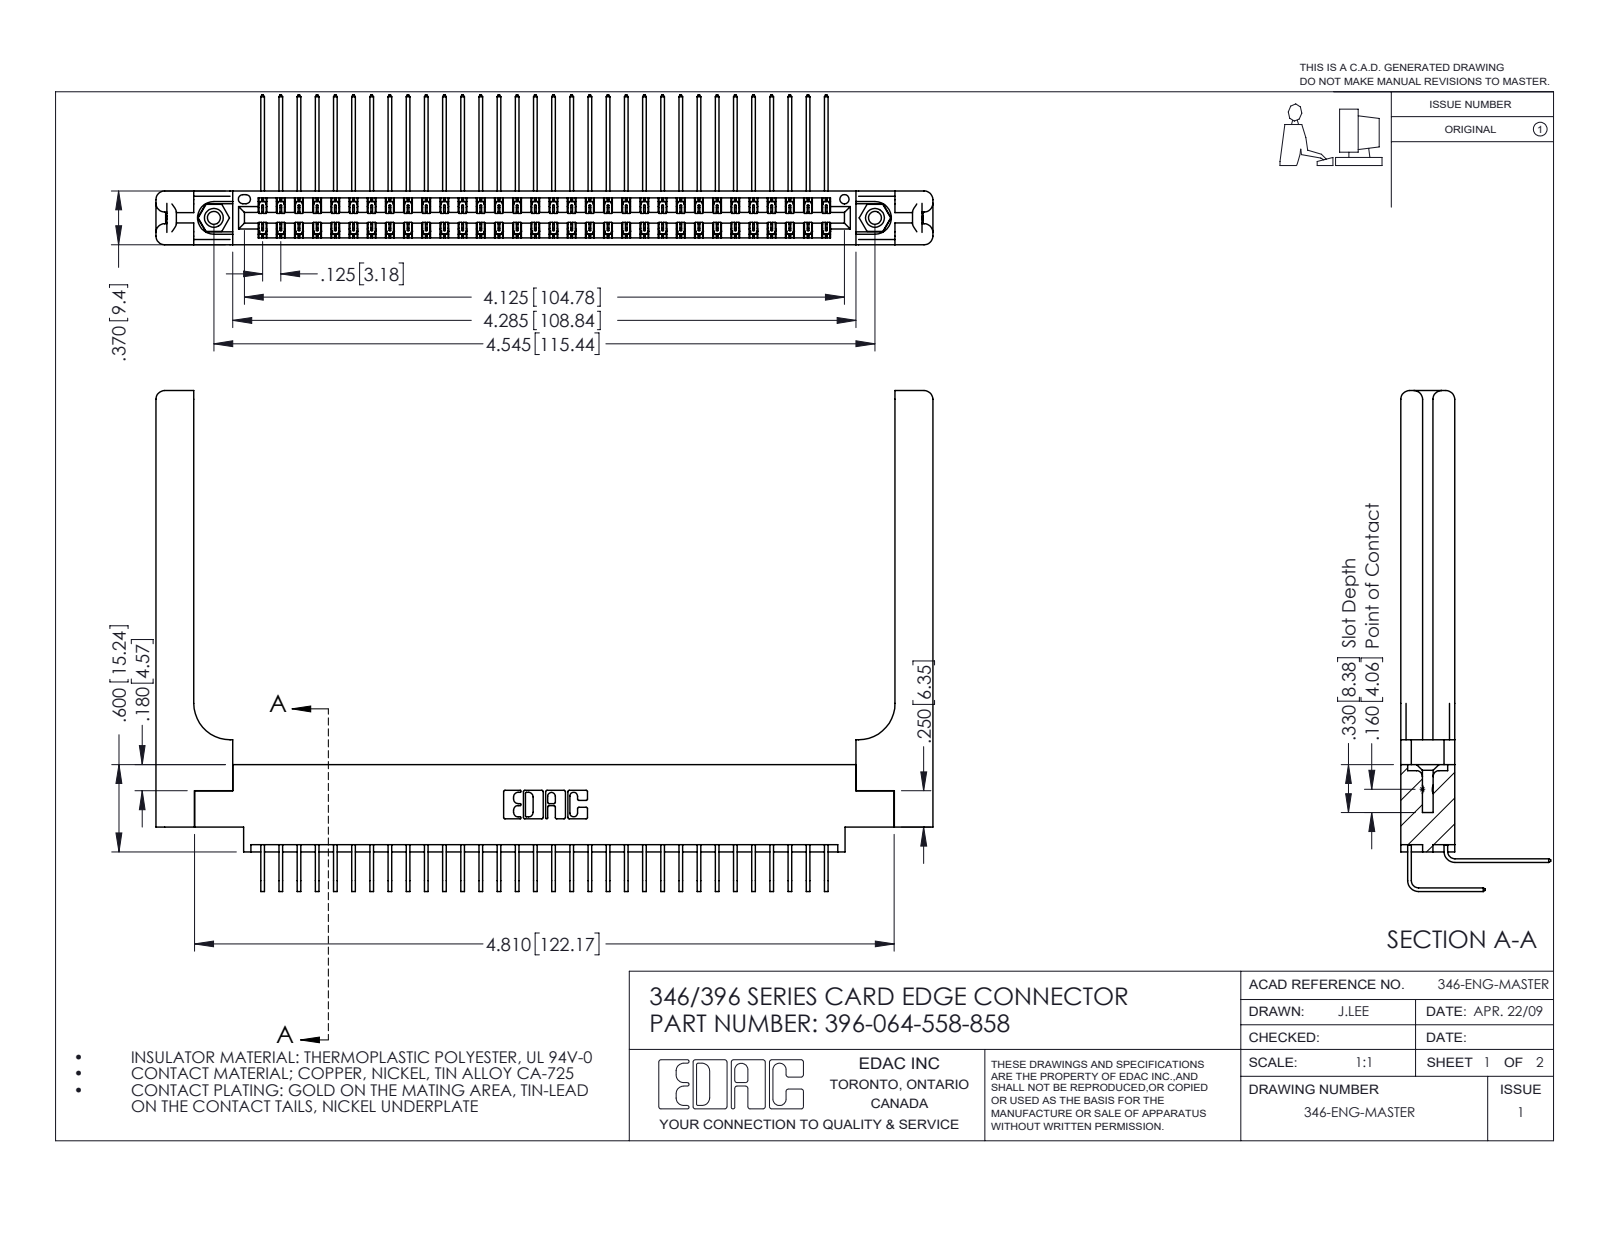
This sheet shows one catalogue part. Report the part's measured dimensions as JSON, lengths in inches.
{"part_name": "346-220-058_345-220-058; 345-250-001_345-250-001-102; 345-292-001_558 Tail - 2; 346 Part_0.170 Offset - 0.156 Dia-TH (+2 more)", "step_written_by": "SolidWorks 2016 (CONFIG_CONTROL_DESIGN)", "units": "inches", "bodies": {"solids": 69, "faces": 3838, "planar": 2596, "cylindrical": 1182, "other": 60}, "overall_size": [5.341, 3.443, 1.03], "volume_in3": 1.273, "surface_area_in2": 38.96, "round_holes": [[0.089, 2], [0.125, 2], [0.156, 2], [0.064, 1]], "round_bosses_or_shafts": [[0.155, 2]], "partial_cylinders_radius": [[0.006, 96], [0.01, 22], [0.06, 16], [0.007, 6], [0.031, 6], [0.026, 3], [0.014, 2], [0.022, 2]], "face_to_face_distances": [0.37, 0.322, 0.048, 0.072, 0.025, 0.148, 0.15, 0.298, 0.25, 0.275], "hole_center_spacings": [0.246, 4.337, 4.545]}
